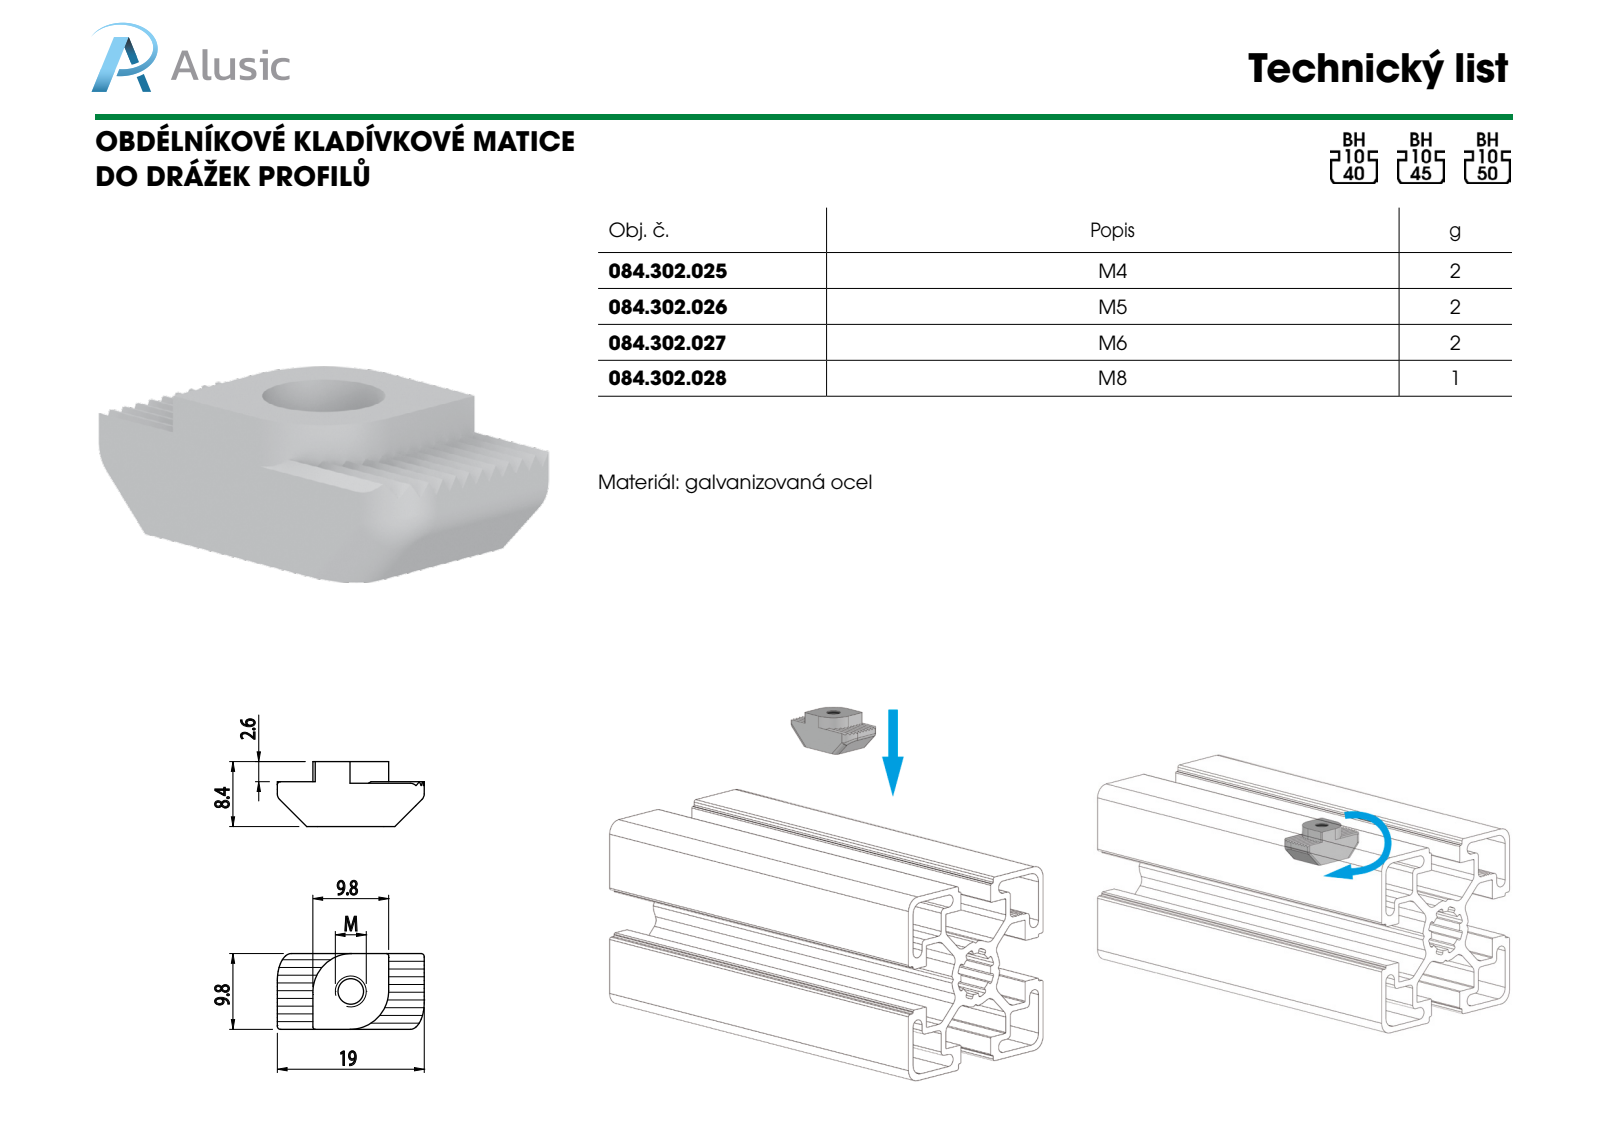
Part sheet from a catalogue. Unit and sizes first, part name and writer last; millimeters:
Units: millimetres
Overall size (bounding box): 20 × 9.8 × 8.6
Round holes (diameter × count): ⌀5 ×1
Partial cylindrical surfaces — rounded edges, fillets, slot ends (radius × count): R3 ×2, R5 ×2
Main face-to-face distances: 9.8, 0.46, 6.47, 8.6, 0.53, 0.92, 6.93, 6.01, 0.99, 7
Volume: 997 mm³ · Surface area: 993 mm²
Bodies: 1 solid, 166 faces (142 planar, 24 cylindrical, 0 other)
Part name (STEP PRODUCT): 084.302.027
STEP written by: SolidWorks 2012 (CONFIG_CONTROL_DESIGN)
